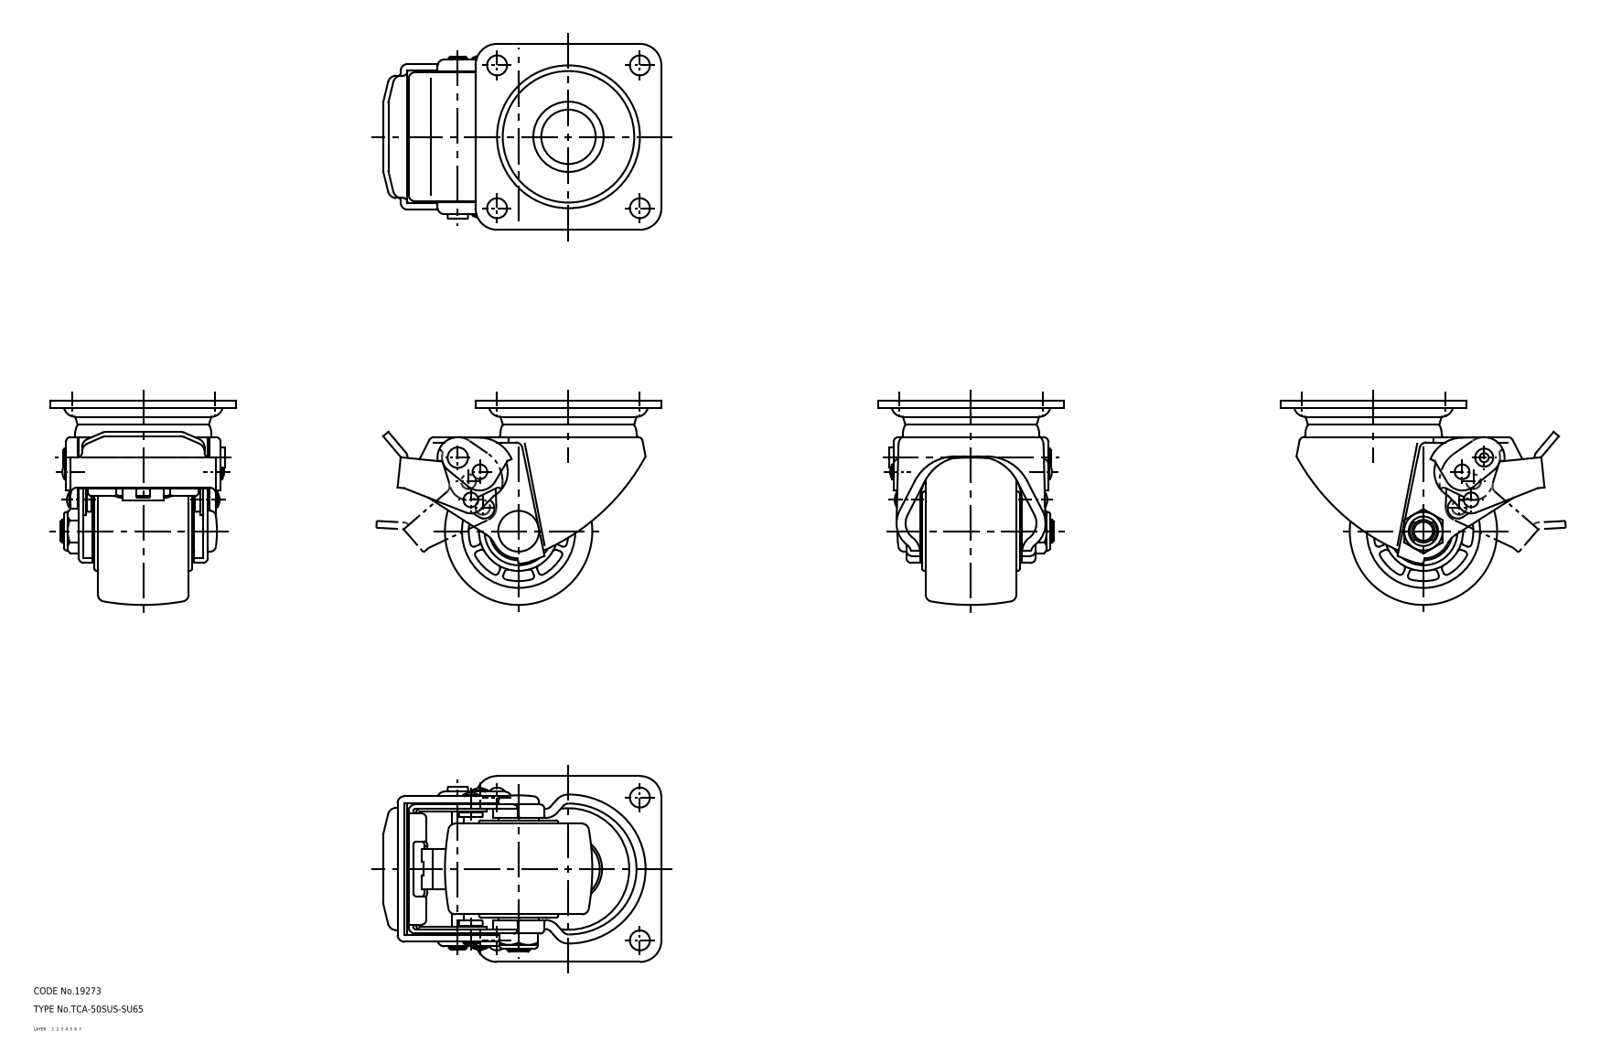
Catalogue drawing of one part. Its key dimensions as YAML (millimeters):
part_name: "67144572; 67144585; 67144598; 67144611 (+6 more)"
step_written_by: "CADfix (AUTOMOTIVE_DESIGN)"
units: millimeters
bodies: {solids: 10, faces: 586, planar: 0, cylindrical: 0, other: 586}
overall_size: [122.73, 90, 82]
volume: 237224
surface_area: 102756
